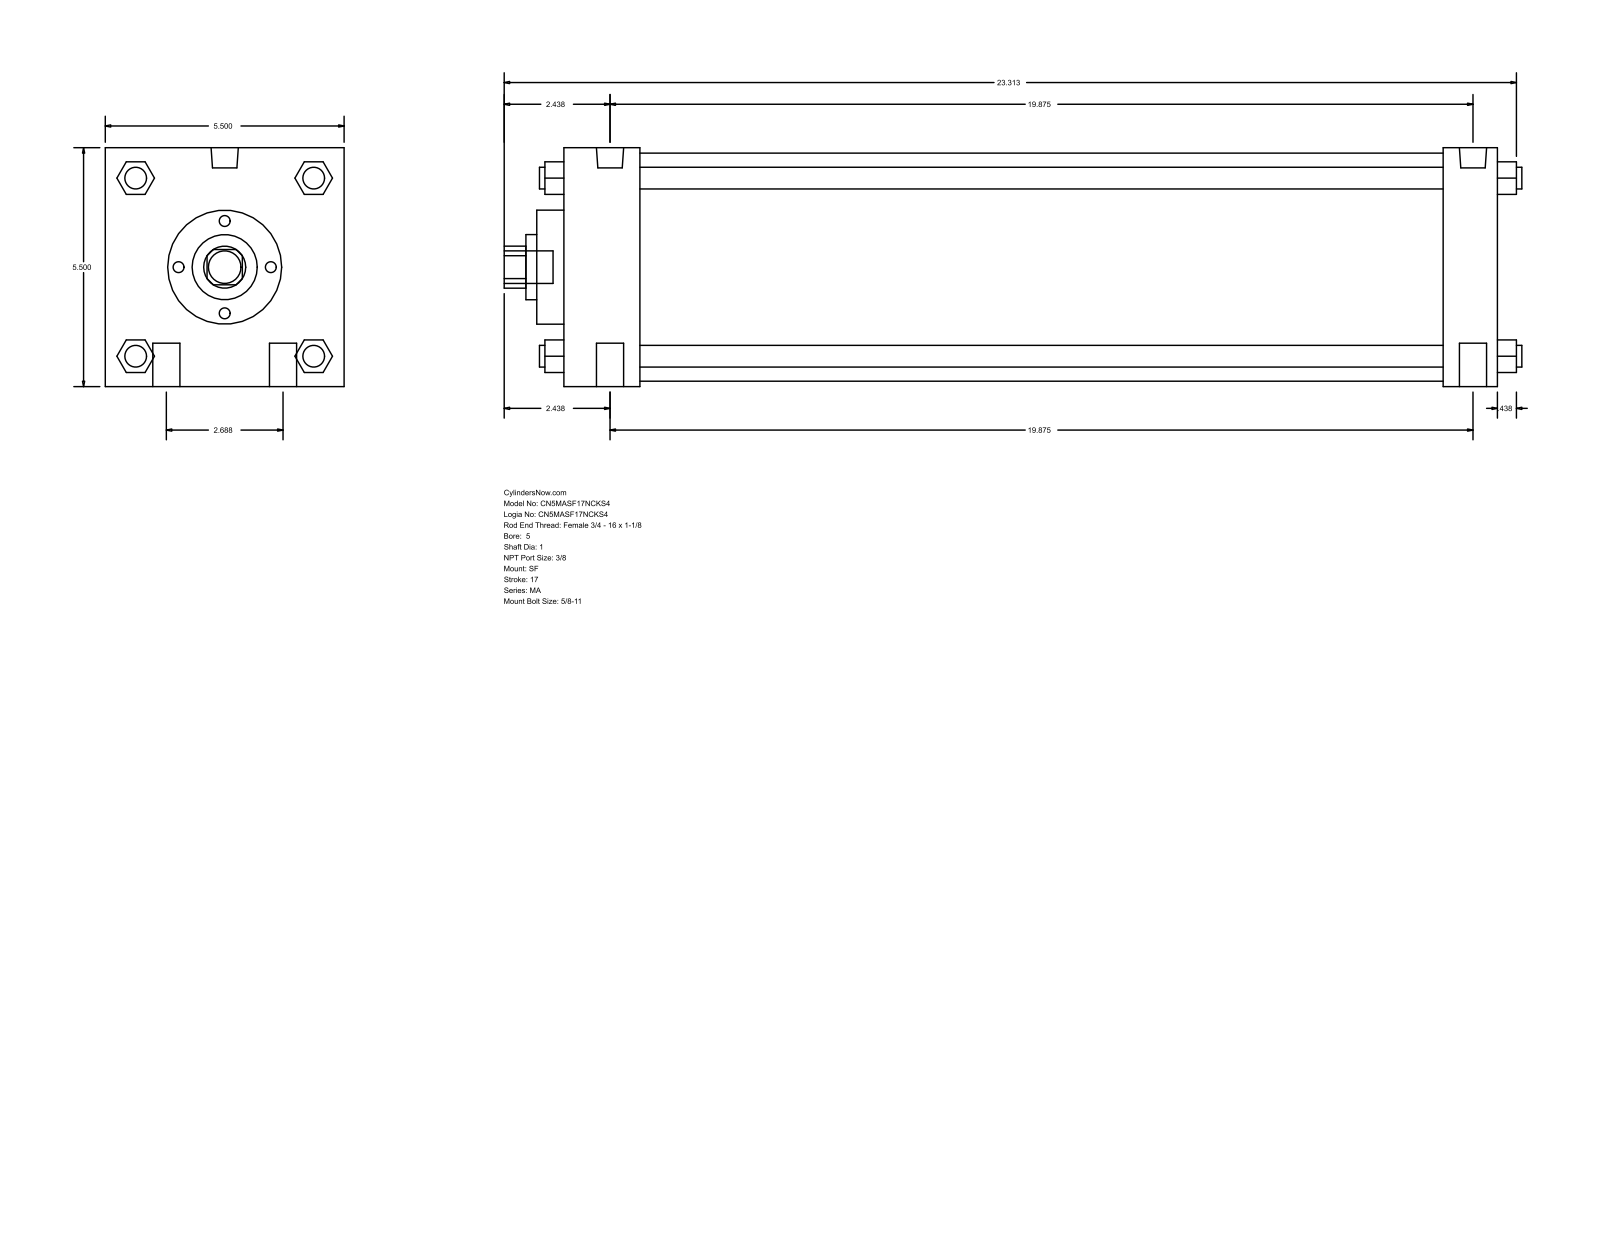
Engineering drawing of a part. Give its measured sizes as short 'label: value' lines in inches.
name: MA_SF__0500_1
written by: GSSL Pune (CONFIG_CONTROL_DESIGN)
unit: in
bodies: 0 solids, 126 faces (95 planar, 31 cylindrical, 0 other)
size: 23.437 × 5.5 × 5.5
holes: 1× ⌀1, 1× ⌀1.5, 1× ⌀2.625, 1× ⌀5.25
bosses: 4× ⌀0.625, 4× ⌀0.5, 2× ⌀0.627, 2× ⌀0.437, 1× ⌀0.75
rounds: 1× R0.484
face distances: 5.5, 21.5, 1.75, 20.25, 18.5, 19.75, 1.25, 0.625, 2.375, 20.875
